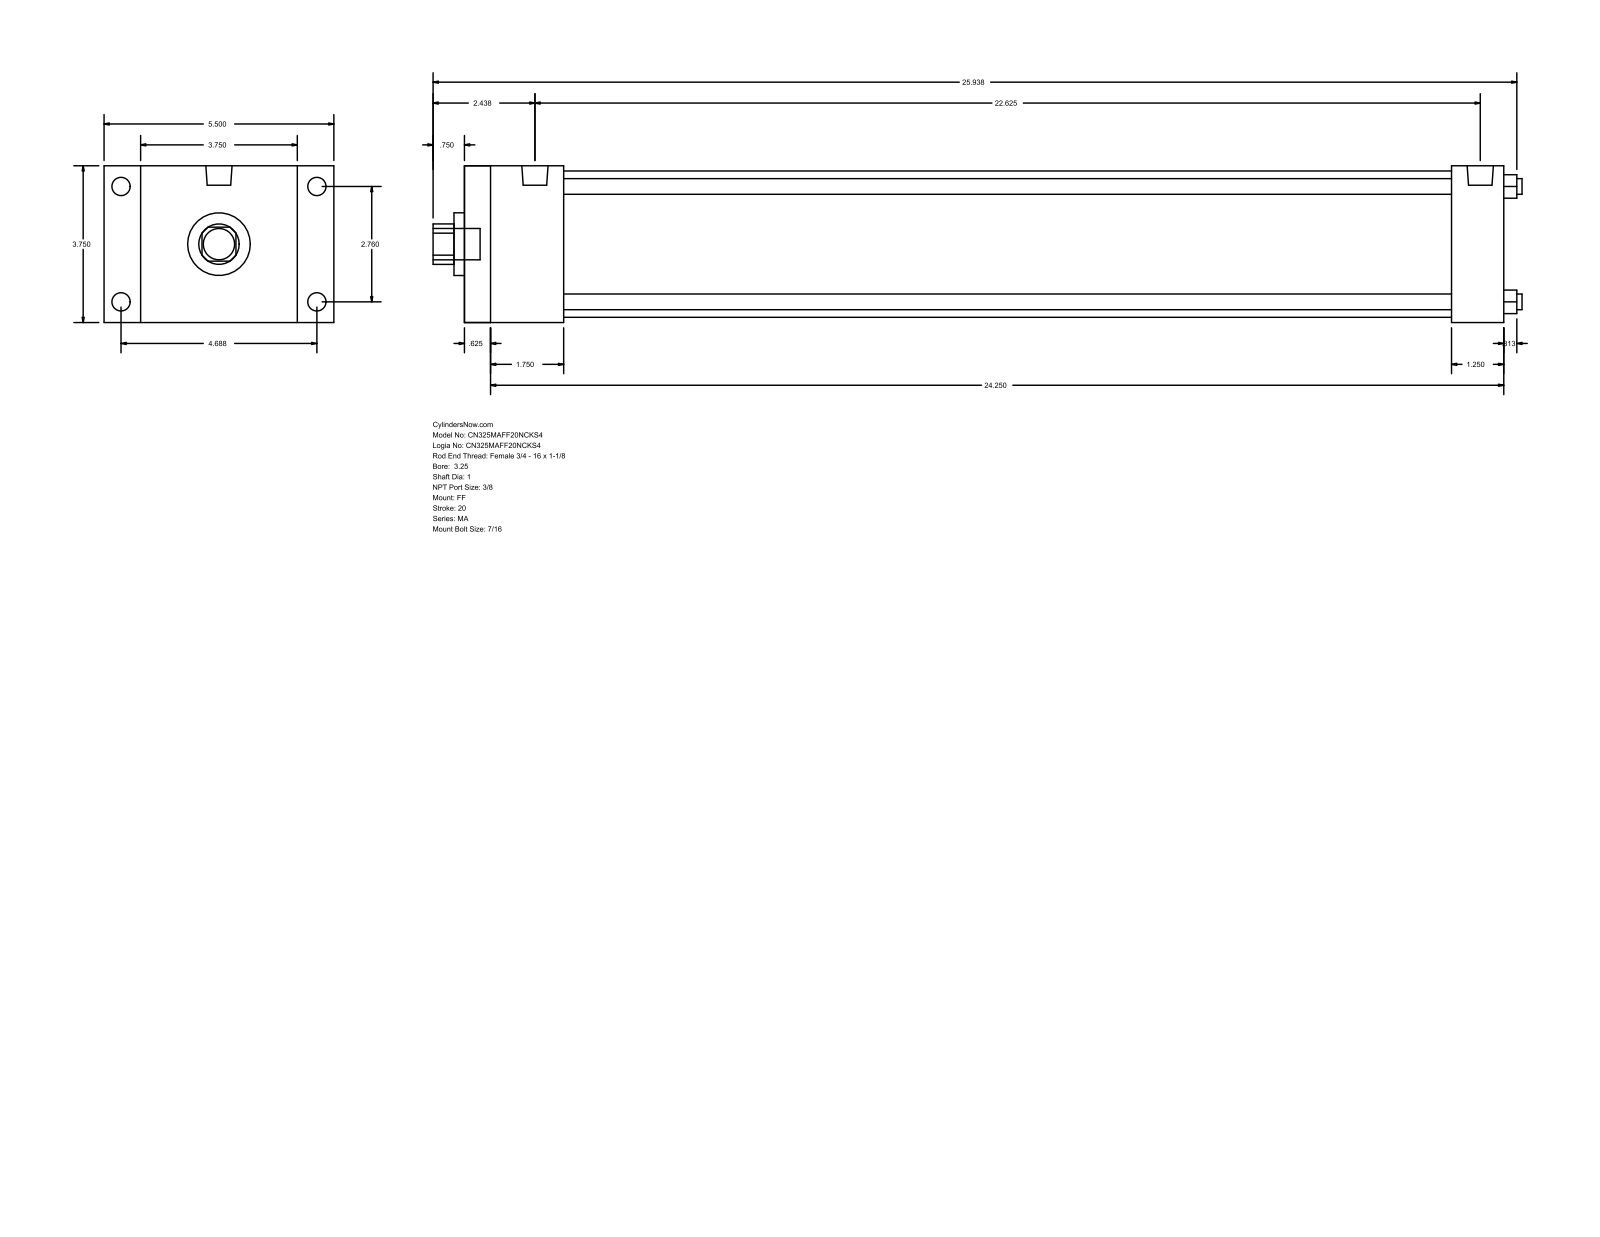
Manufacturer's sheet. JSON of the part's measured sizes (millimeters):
{"part_name": "MA_FF__0325_1", "step_written_by": "GSSL Pune (CONFIG_CONTROL_DESIGN)", "units": "millimeters", "bodies": {"solids": 0, "faces": 92, "planar": 64, "cylindrical": 28, "other": 0}, "overall_size": [661.99, 139.7, 95.25], "round_holes": [[9.53, 4], [25.4, 1], [38.1, 1], [88.9, 1]], "round_bosses_or_shafts": [[11.11, 8], [15.93, 2], [19.05, 1]], "partial_cylinders_radius": [[12.29, 1]], "face_to_face_distances": [95.24, 631.83, 15.87, 615.96, 22.23, 117.47, 60.33, 600.07, 44.46, 584.2], "hole_center_spacings": [49.57, 70.1, 99.14]}
